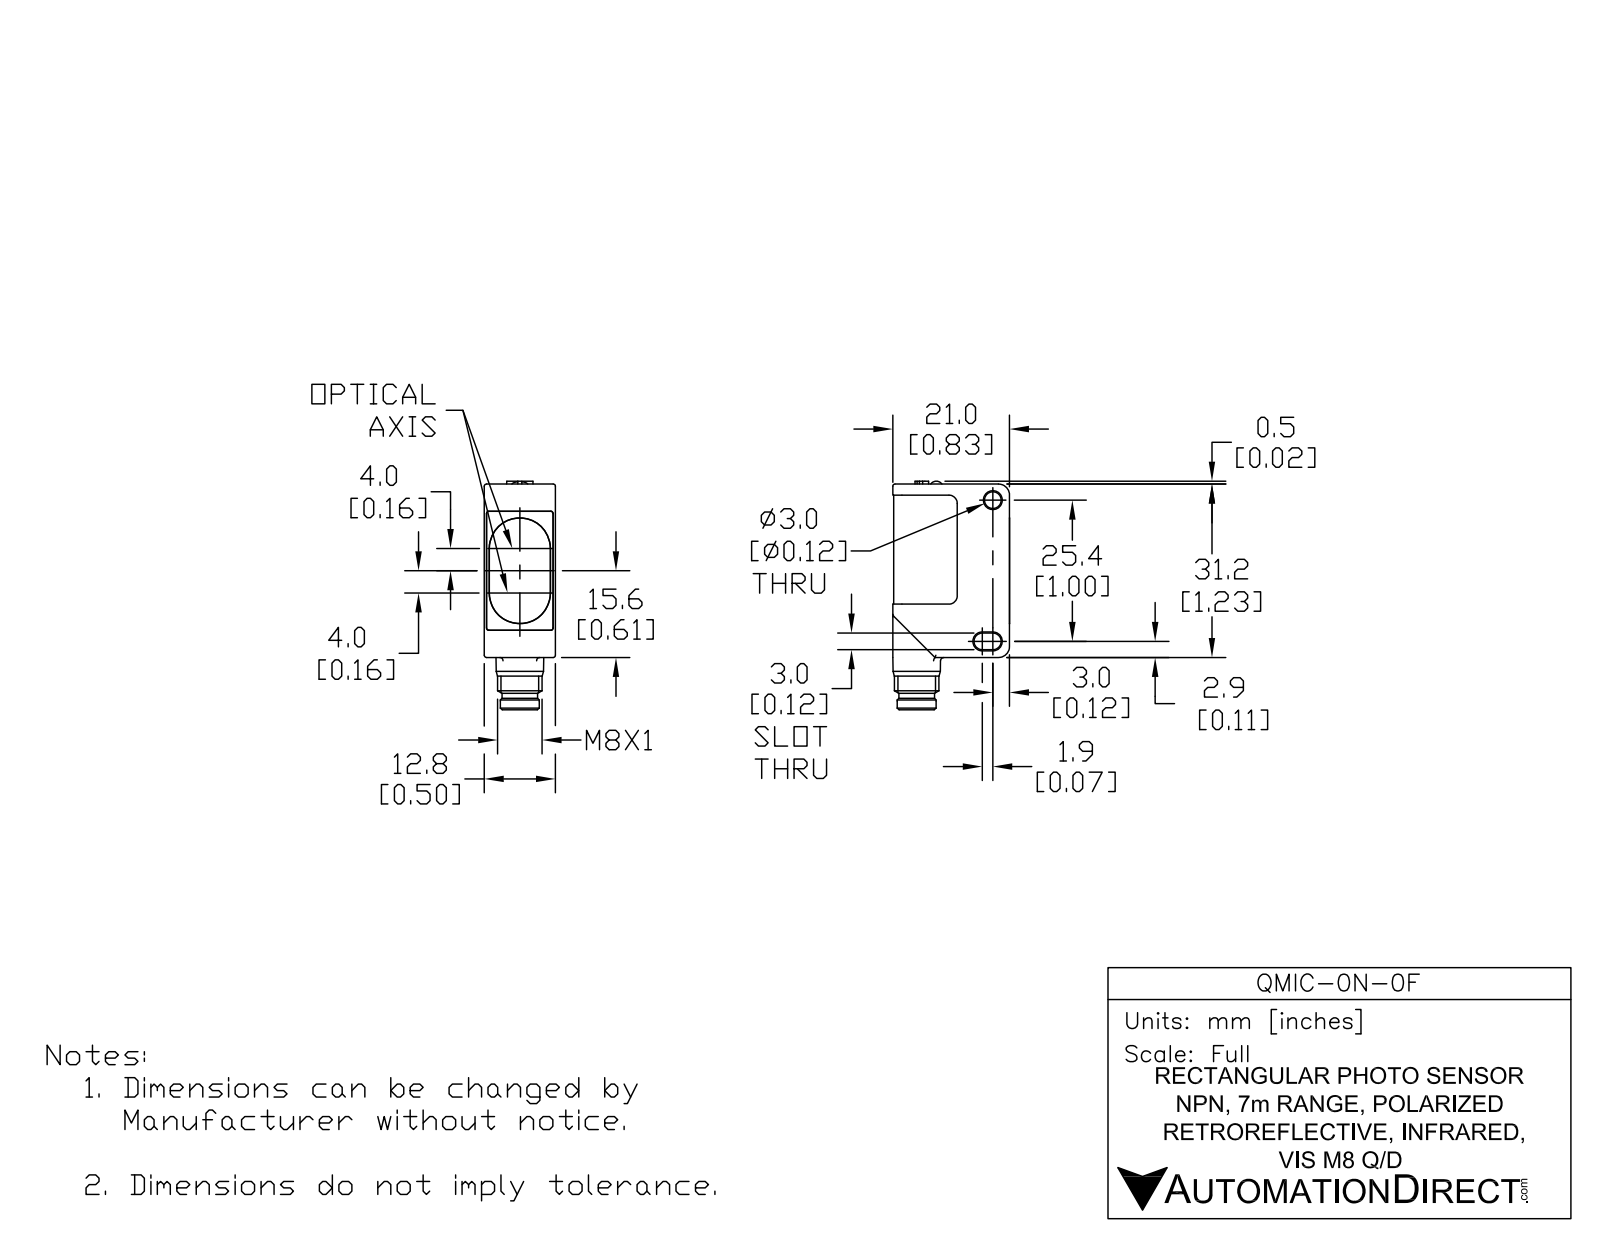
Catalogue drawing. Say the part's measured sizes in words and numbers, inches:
The part is named "QMIC-0N-0F". Its 3-D file was written by "SolidWorks 2017 (AUTOMOTIVE_DESIGN)". It is 7 solids with 272 faces: 125 planar, 100 cylindrical and 47 other. Overall it measures 1.619 by 0.827 by 0.504 inches. Its volume is 0.474 cubic inches and its surface area 7.749 square inches. Round holes: 3 of diameter 0.118, 1 of diameter 0.228. Round bosses or shafts: 4 of diameter 0.039, 2 of diameter 0.138, 1 of diameter 0.315, 1 of diameter 0.276, 1 of diameter 0.252. Partial cylindrical surfaces (rounded edges, fillets, slot ends): 10 of radius 0.016, 9 of radius 0.02, 6 of radius 0.059, 4 of radius 0.024, 4 of radius 0.039, 2 of radius 0.006, 2 of radius 0.044, 2 of radius 0.065. The main face-to-face distances are 0.498, 0.02, 0.504, 0.11, 0.016, 0.492, 0.488, 0.482, 0.059, 0.711. The hole center spacings are 0.04, 0.205, 0.245.
